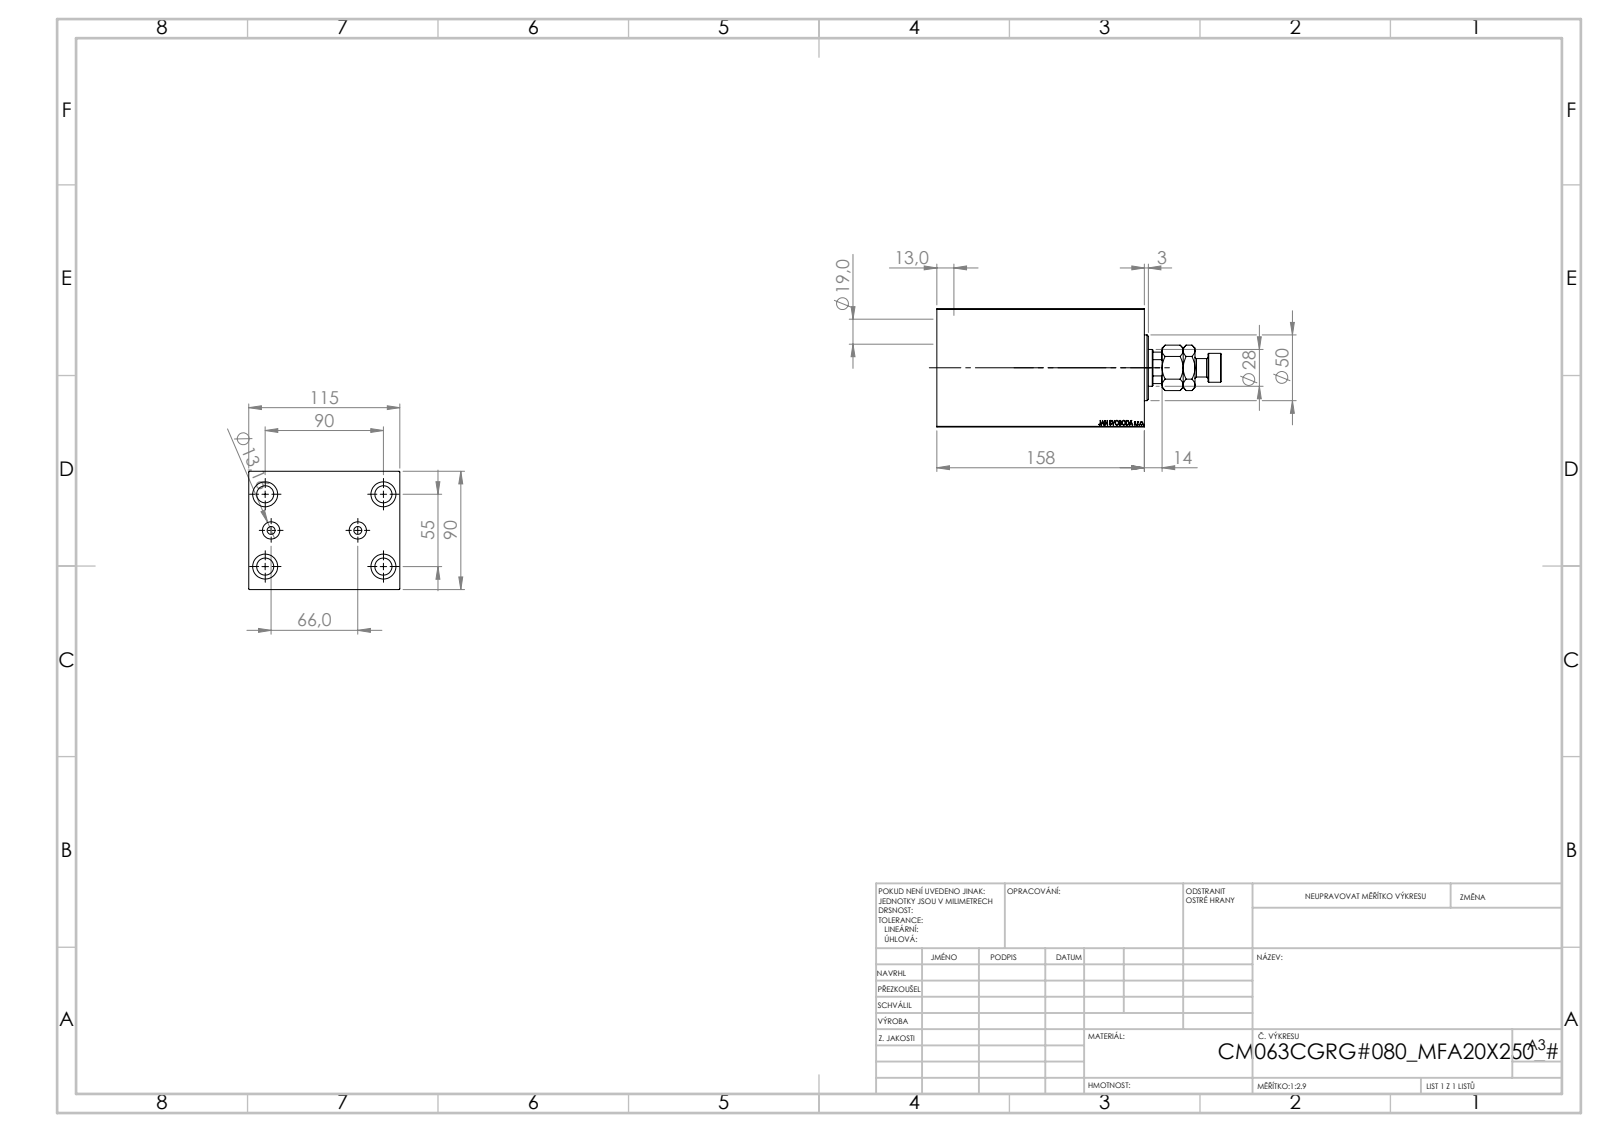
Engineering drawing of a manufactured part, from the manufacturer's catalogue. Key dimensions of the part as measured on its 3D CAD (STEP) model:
Part name (STEP PRODUCT): V450CM_C_VCP; MFA; V450CM_VC_B; V450CM_C_Body
STEP written by: SolidWorks 2019 (CONFIG_CONTROL_DESIGN)
Units: millimetres
Bodies: 4 solids, 913 faces (425 planar, 62 cylindrical, 426 other)
Overall size (bounding box): 216.5 × 115 × 90
Volume: 1 355 000 mm³ · Surface area: 189 536 mm²
Round holes (diameter × count): ⌀13 ×4, ⌀19 ×4, ⌀6 ×2, ⌀13.16 ×2, ⌀18.5 ×1, ⌀28 ×1, ⌀31.5 ×1, ⌀63 ×1, ⌀65 ×1, ⌀72 ×1
Round bosses / shafts (diameter × count): ⌀50 ×1, ⌀22 ×1, ⌀14 ×1
Partial cylindrical surfaces — rounded edges, fillets, slot ends (radius × count): R13.5 ×1
Main face-to-face distances: 90, 115, 158, 17.5, 140.5, 29.3, 111.2, 128.7, 80, 109.3
Hole centre spacings: 30, 52.74, 82.71, 33, 55, 90, 105.48, 66
